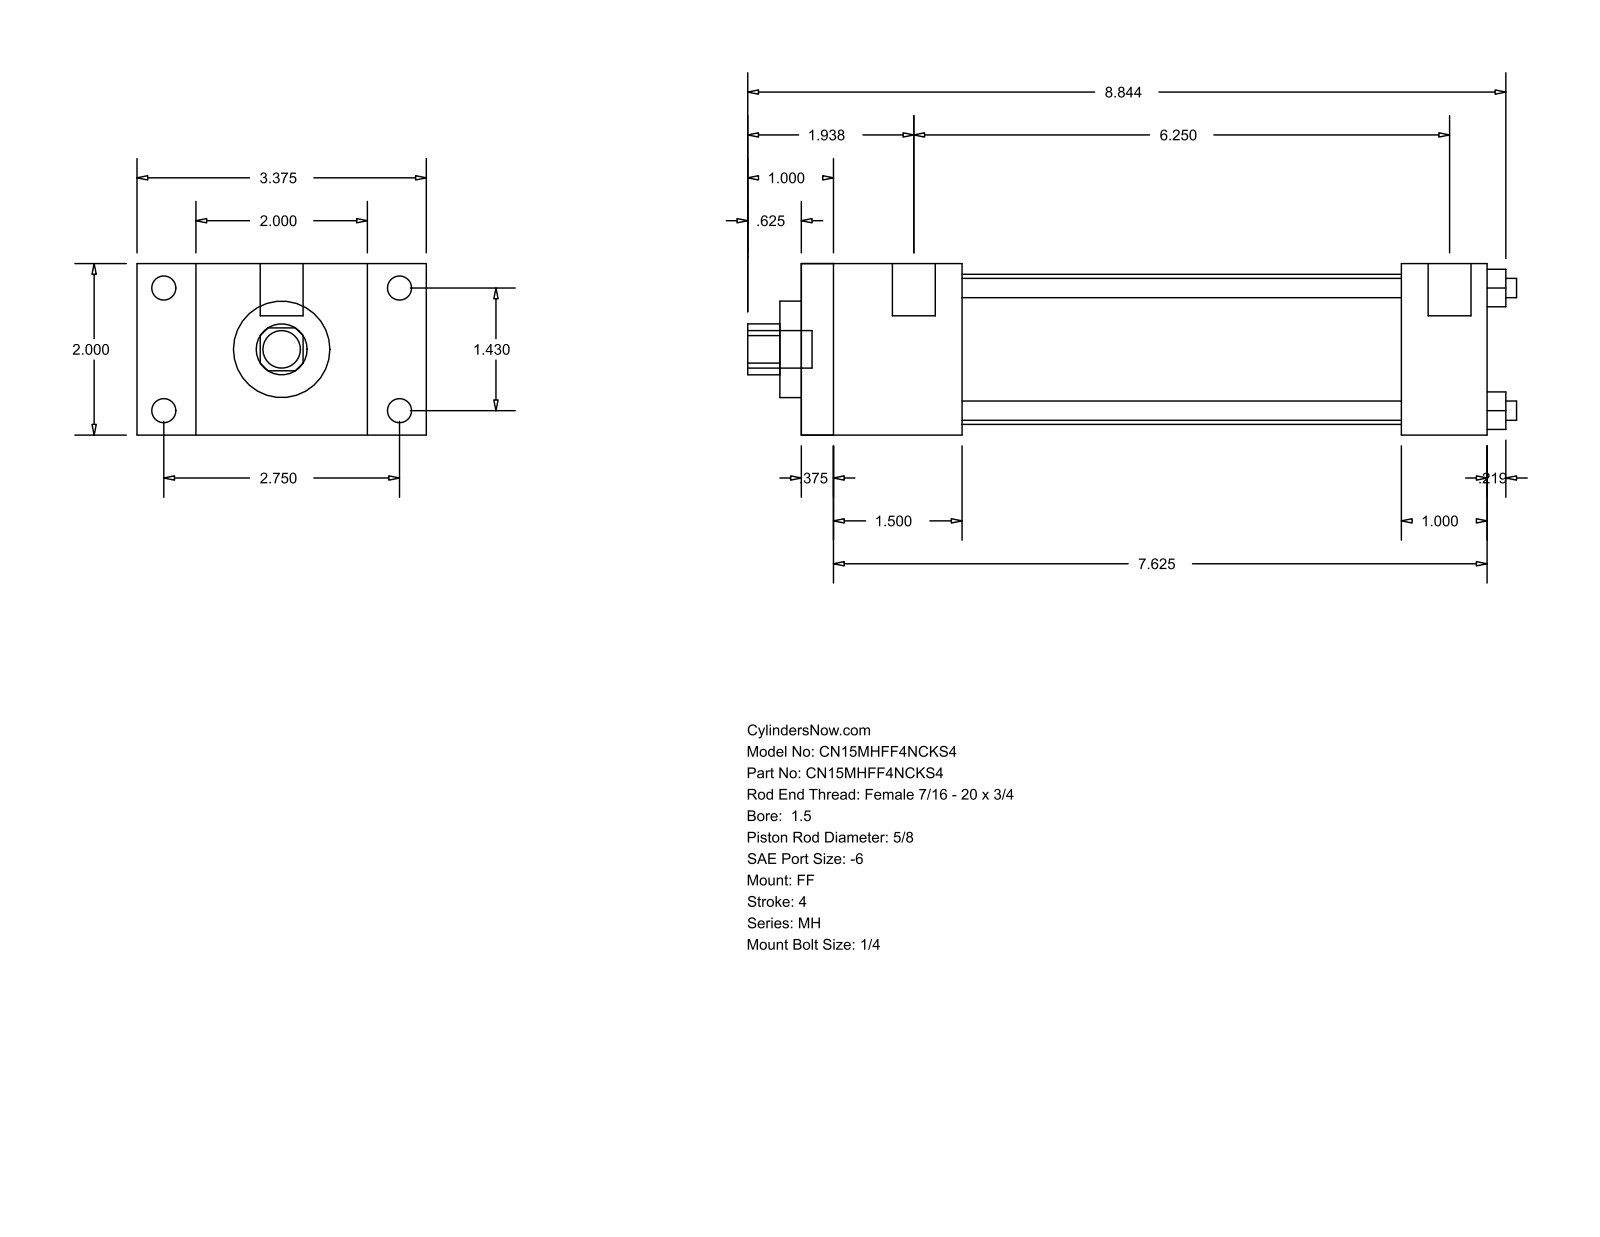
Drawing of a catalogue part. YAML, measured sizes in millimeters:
part_name: "MH_FF__0150_0.625"
step_written_by: "GSSL Pune (CONFIG_CONTROL_DESIGN)"
units: millimeters
bodies: {solids: 0, faces: 92, planar: 64, cylindrical: 28, other: 0}
overall_size: [227.81, 85.72, 50.8]
round_holes:
  - {diameter: 5.71, count: 4}
  - {diameter: 15.88, count: 1}
  - {diameter: 28.57, count: 1}
  - {diameter: 44.45, count: 1}
round_bosses_or_shafts:
  - {diameter: 7.14, count: 4}
  - {diameter: 5.56, count: 4}
  - {diameter: 12.7, count: 2}
  - {diameter: 11.11, count: 1}
partial_cylinders:
  - {radius: 7.54, count: 1}
face_to_face_distances: [50.8, 203.19, 9.52, 193.67, 17.46, 68.26, 47.62, 38.1, 155.57, 177.8]
hole_center_spacings: [25.68, 36.32, 51.36]
